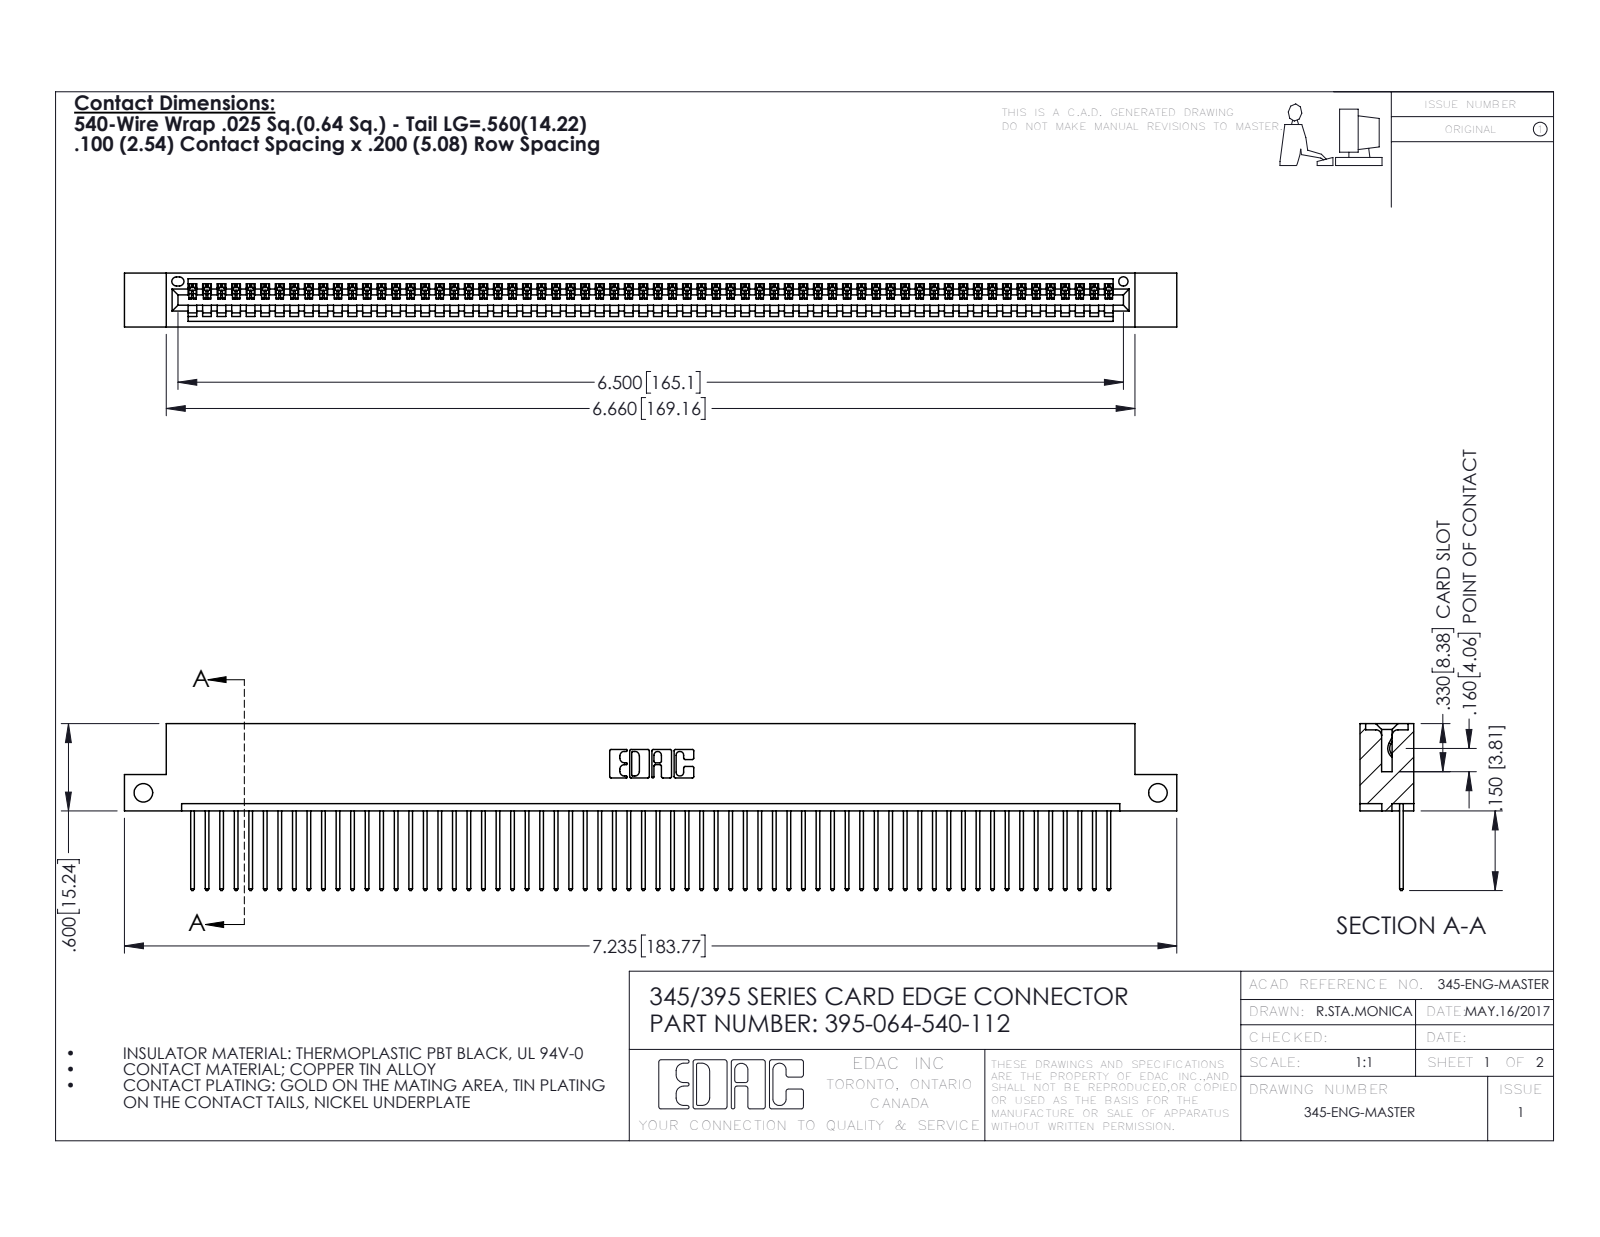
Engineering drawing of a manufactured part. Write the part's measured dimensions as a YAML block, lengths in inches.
part_name: "345-292-001_345-293-140; 345 Part_Flush Mounting Lugs - Side Mount; 395-064-540-112"
step_written_by: "SolidWorks 2016 (CONFIG_CONTROL_DESIGN)"
units: inches
bodies: {solids: 65, faces: 3838, planar: 2640, cylindrical: 1198, other: 0}
overall_size: [7.235, 1.147, 0.37]
volume: 1.076
surface_area: 37.53
round_holes:
  - {diameter: 0.128, count: 2}
  - {diameter: 0.064, count: 1}
partial_cylinders:
  - {radius: 0.006, count: 128}
  - {radius: 0.01, count: 128}
  - {radius: 0.01, count: 22}
  - {radius: 0.007, count: 6}
  - {radius: 0.031, count: 6}
  - {radius: 0.026, count: 3}
  - {radius: 0.031, count: 2}
  - {radius: 0.04, count: 2}
face_to_face_distances: [0.072, 0.298, 0.37, 0.098, 0.272, 0.025, 0.2, 0.225, 0.149, 0.072]
hole_center_spacings: [6.975]
